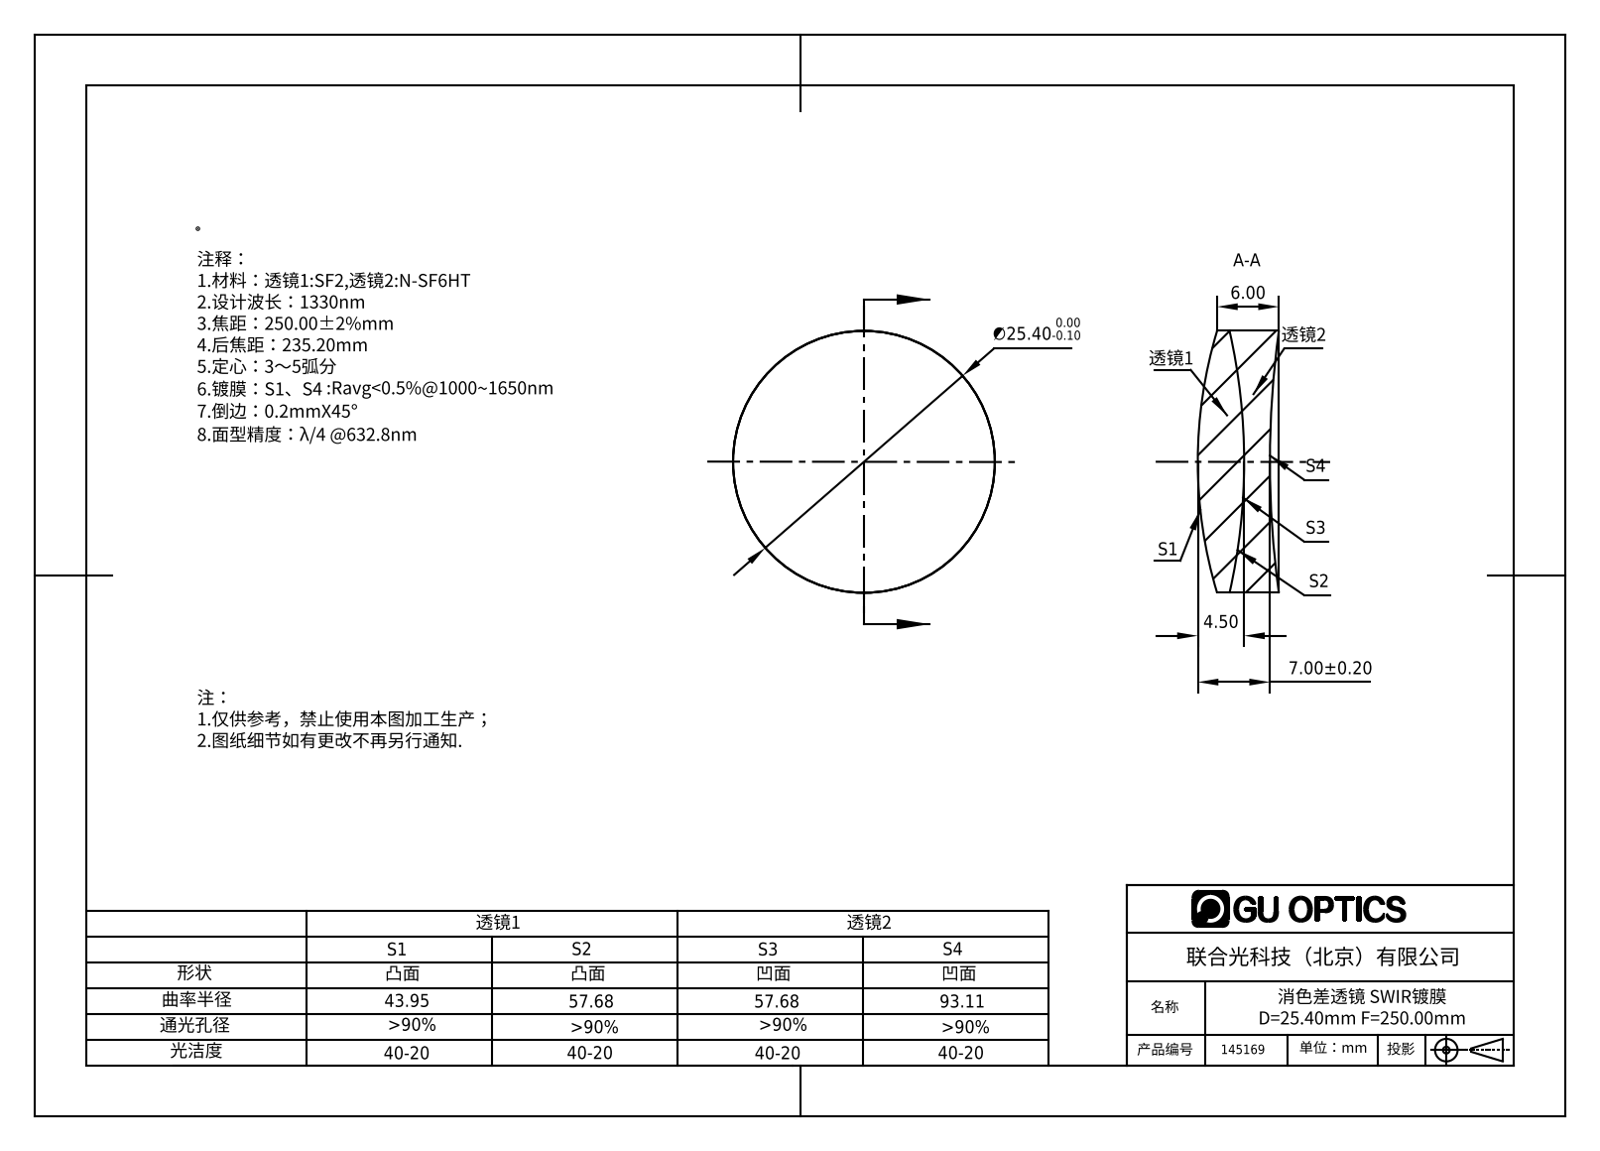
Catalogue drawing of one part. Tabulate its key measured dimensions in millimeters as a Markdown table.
| quantity | value |
| --- | --- |
| part name | 145169 |
| STEP written by | SolidWorks 2016 (AUTOMOTIVE_DESIGN) |
| units | millimeters |
| bodies | 2 solids, 12 faces (0 planar, 4 cylindrical, 8 other) |
| overall size | 25.4 × 25.4 × 7.87 |
| volume | 3 296 mm³ |
| surface area | 2 531 mm² |
| round bosses / shafts (diameter × count) | 25.4 × 1 |
